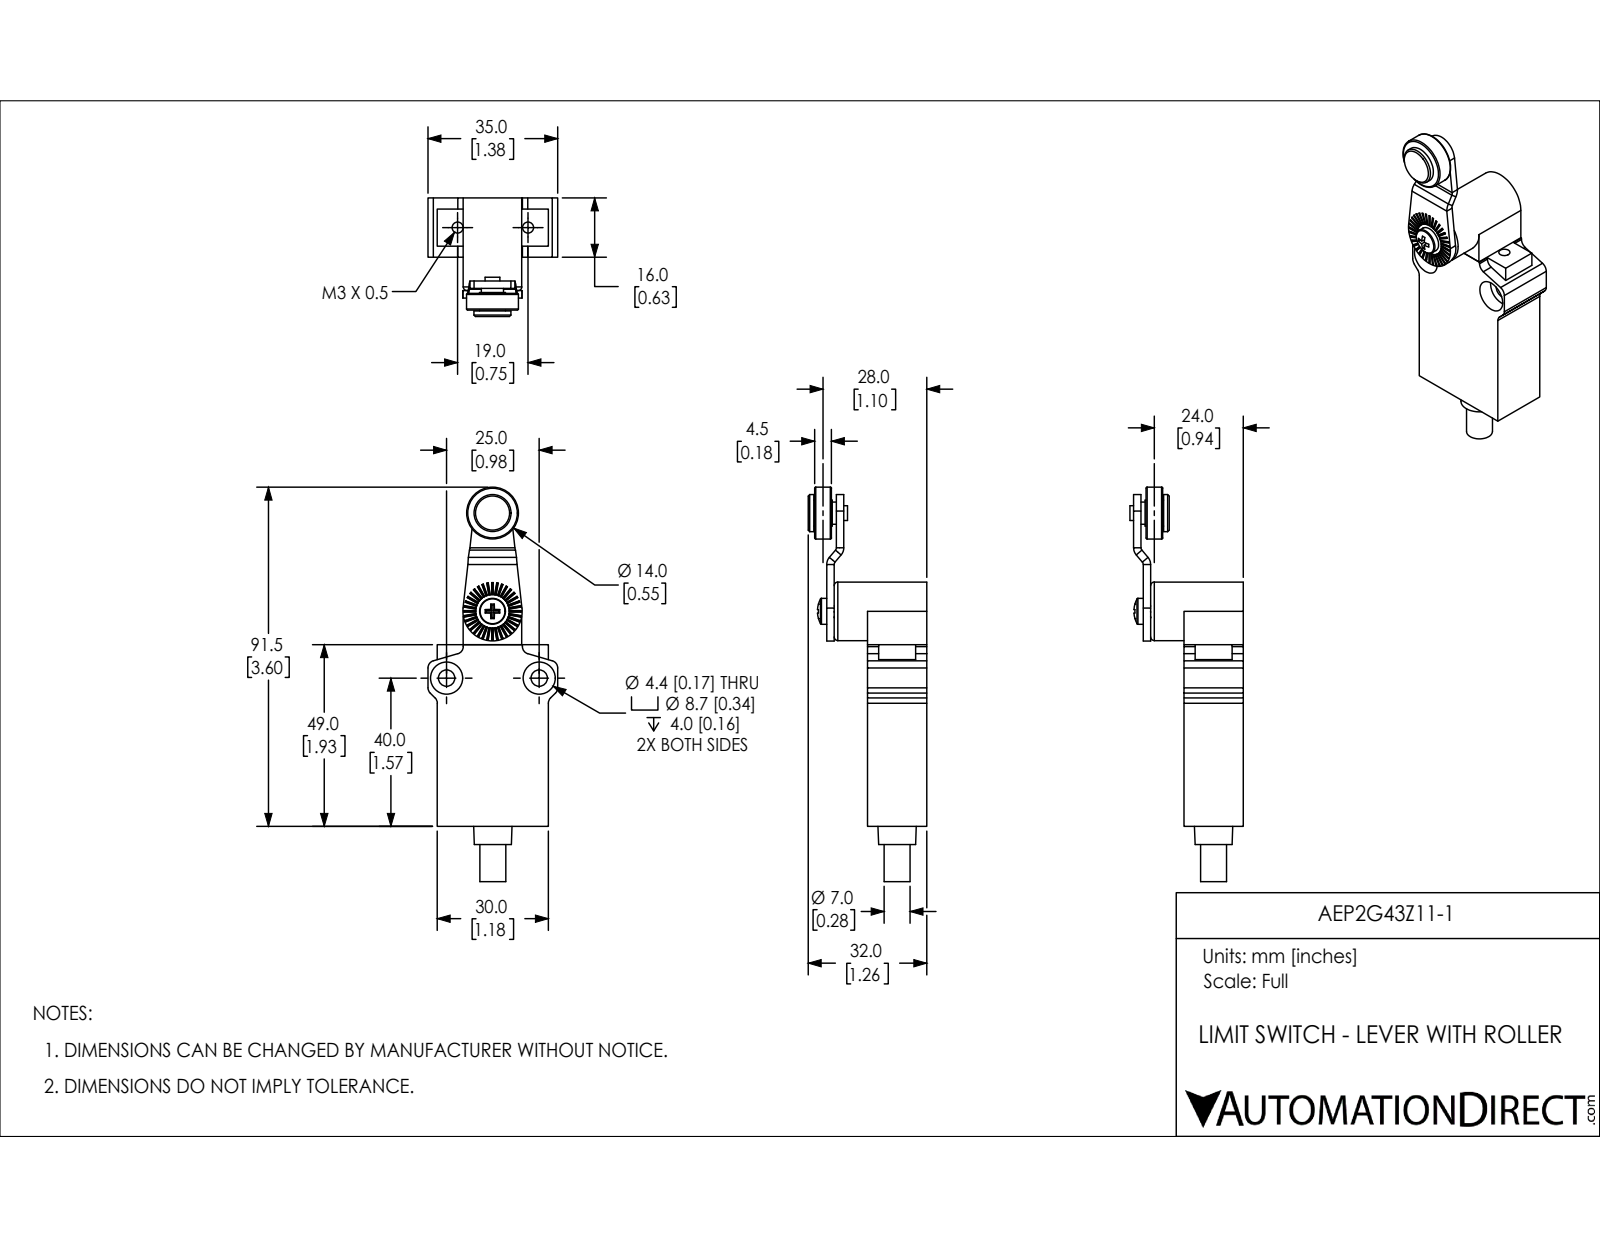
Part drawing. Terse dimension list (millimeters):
name: AEP2G43Z11-1
written by: SolidWorks 2018 (AUTOMOTIVE_DESIGN)
unit: mm
bodies: 6 solids, 584 faces (295 planar, 117 cylindrical, 172 other)
size: 106.4 × 35 × 32
volume: 30 460 mm³; area: 11 310 mm²
holes: 2× ⌀3, 2× ⌀4.4, 2× ⌀8.7, 1× ⌀2.5, 1× ⌀4.1, 1× ⌀5, 1× ⌀5.7
bosses: 3× ⌀7, 1× ⌀15.8, 1× ⌀14, 1× ⌀10, 1× ⌀6, 1× ⌀4, 1× ⌀3.5
rounds: 8× R2, 2× R1, 2× R3, 1× R6.5, 1× R8
face distances: 16, 30, 9, 49, 2, 25, 2.6, 12, 23, 7
hole spacings: 19, 21.9, 22, 25, 26.5, 46.2, 46.3
